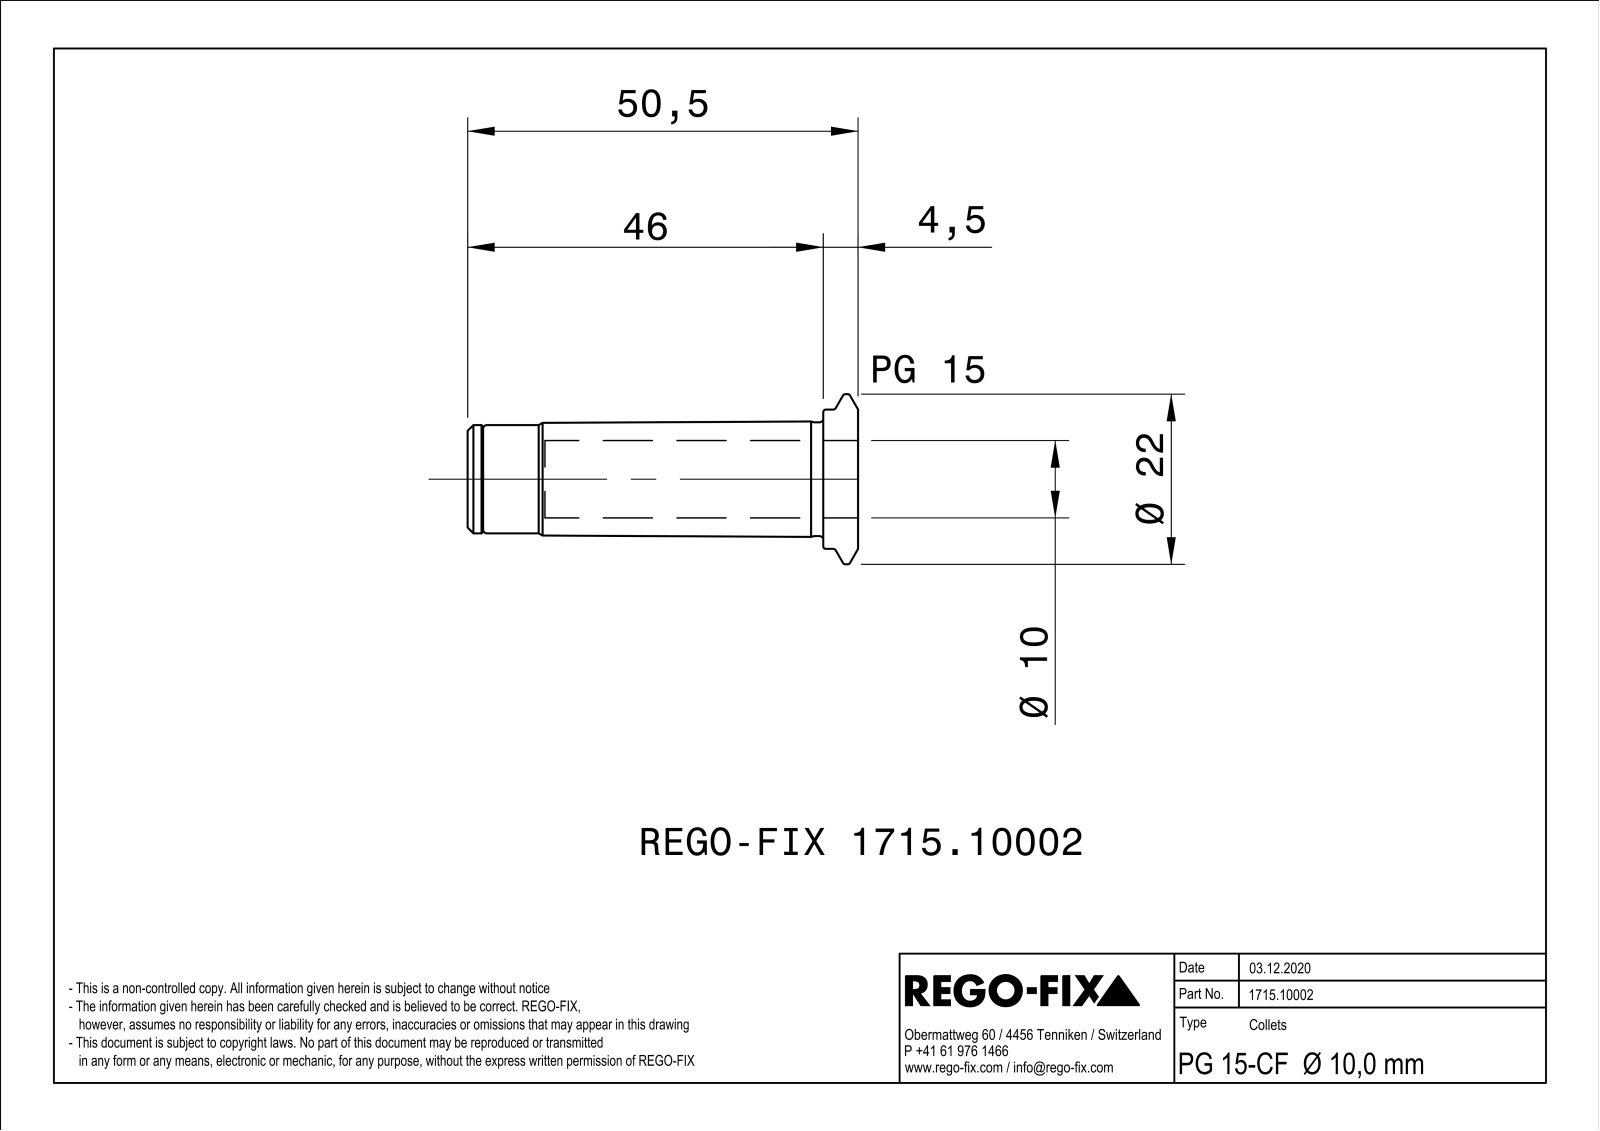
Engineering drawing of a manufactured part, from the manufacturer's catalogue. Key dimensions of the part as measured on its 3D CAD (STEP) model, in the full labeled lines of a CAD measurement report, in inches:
Part name (STEP PRODUCT): NOCUT
STEP written by: SIEMENS PLM Software Solid Edge ST10 (AUTOMOTIVE_DESIGN)
Units: inches
Bodies: 1 solid, 125 faces (41 planar, 35 cylindrical, 49 other)
Overall size (bounding box): 1.988 × 0.866 × 0.866
Volume: 0.305 in³ · Surface area: 8.313 in²
Round holes (diameter × count): ⌀0.205 ×1, ⌀0.272 ×1, ⌀0.323 ×1, ⌀0.394 ×1, ⌀0.43 ×1, ⌀0.48 ×1
Round bosses / shafts (diameter × count): ⌀0.866 ×1, ⌀0.709 ×1, ⌀0.579 ×1, ⌀0.551 ×1
Partial cylindrical surfaces — rounded edges, fillets, slot ends (radius × count): R0.02 ×3, R0.205 ×1, R0.236 ×1
Main face-to-face distances: 0.039, 0.079, 1.988, 1.594, 0.394, 1.634, 0.354, 0.118, 0.177, 1.417
